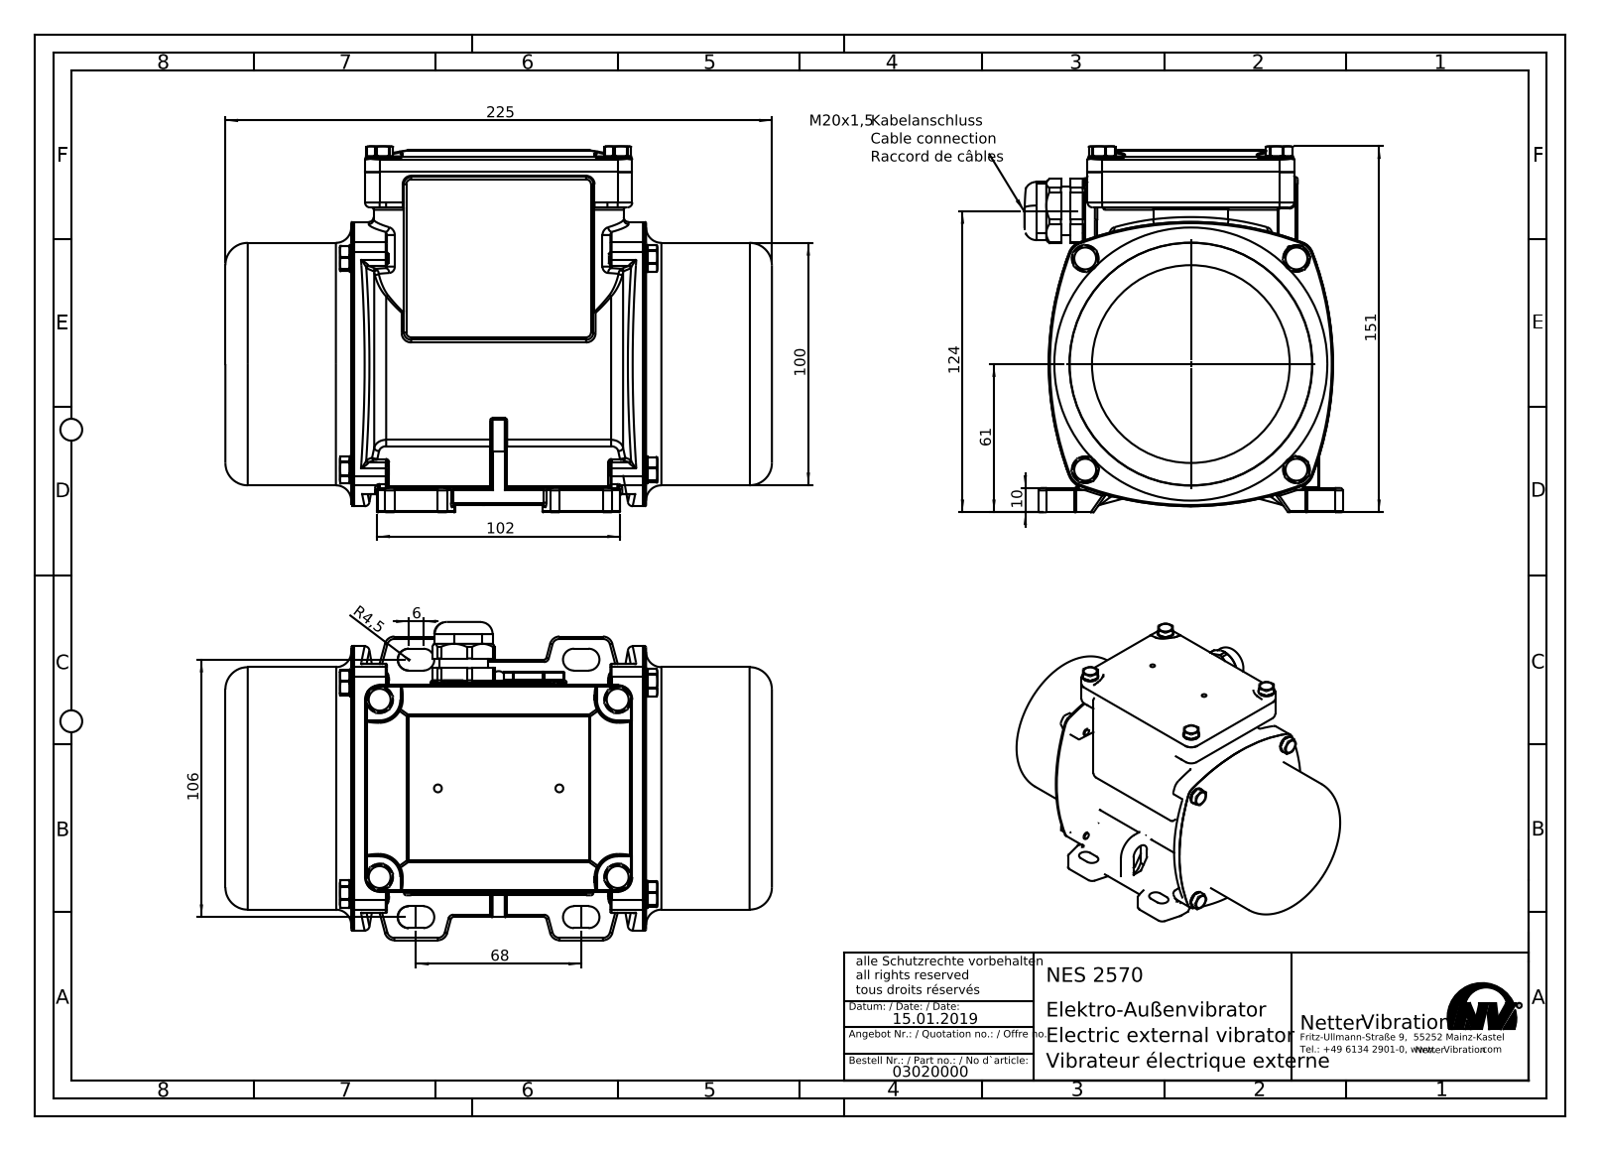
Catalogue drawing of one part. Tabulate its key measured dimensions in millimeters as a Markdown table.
| quantity | value |
| --- | --- |
| part name | NES 2570 #03020000 |
| STEP written by | SolidWorks 2015 (CONFIG_CONTROL_DESIGN) |
| units | millimeters |
| bodies | 0 solids, 2816 faces (1116 planar, 0 cylindrical, 1700 other) |
| overall size | 225 × 150.7 × 131 |
| main face-to-face distances | 130, 11, 119, 42, 53, 172, 183, 141, 15, 9 |
